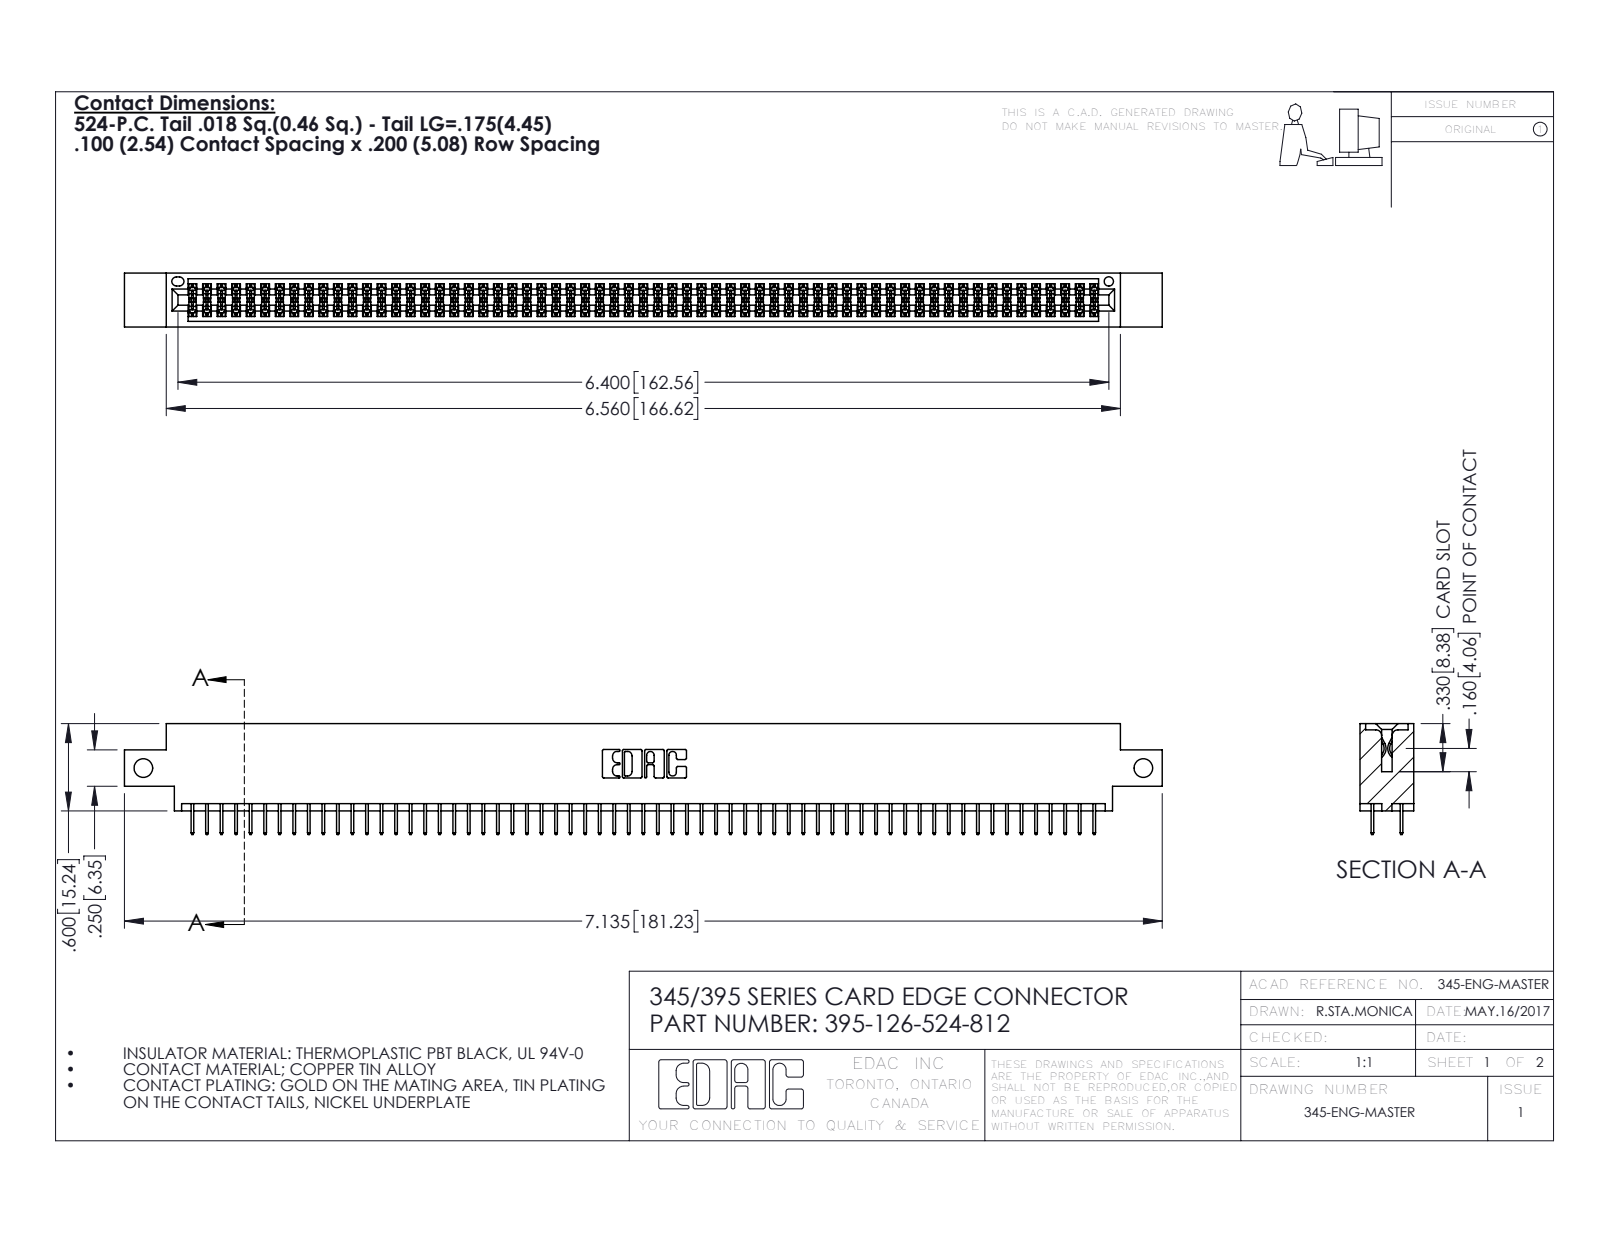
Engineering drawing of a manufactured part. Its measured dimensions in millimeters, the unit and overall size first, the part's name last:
Units: millimetres
Overall size (bounding box): 181.2 × 19.4 × 9.4
Round holes (diameter × count): ⌀3.3 ×2, ⌀1.6 ×1
Partial cylindrical surfaces — rounded edges, fillets, slot ends (radius × count): R0.2 ×189, R0.3 ×22, R0.2 ×6, R0.8 ×6, R0.7 ×3, R0.4 ×2, R0.5 ×2, R0.6 ×2
Main face-to-face distances: 1.8, 7.6, 9.4, 5.1, 2.5, 6.9, 0.6, 5.7, 1.8, 4.4
Hole centre spacings: 174.6
Volume: 17 400 mm³ · Surface area: 25 650 mm²
Bodies: 127 solids, 6934 faces (4998 planar, 1936 cylindrical, 0 other)
Part name (STEP PRODUCT): 345-292-001_345-293-124; 345 Part_0.170 Offset - Side Mount; 395-126-524-812
STEP written by: SolidWorks 2016 (CONFIG_CONTROL_DESIGN)
